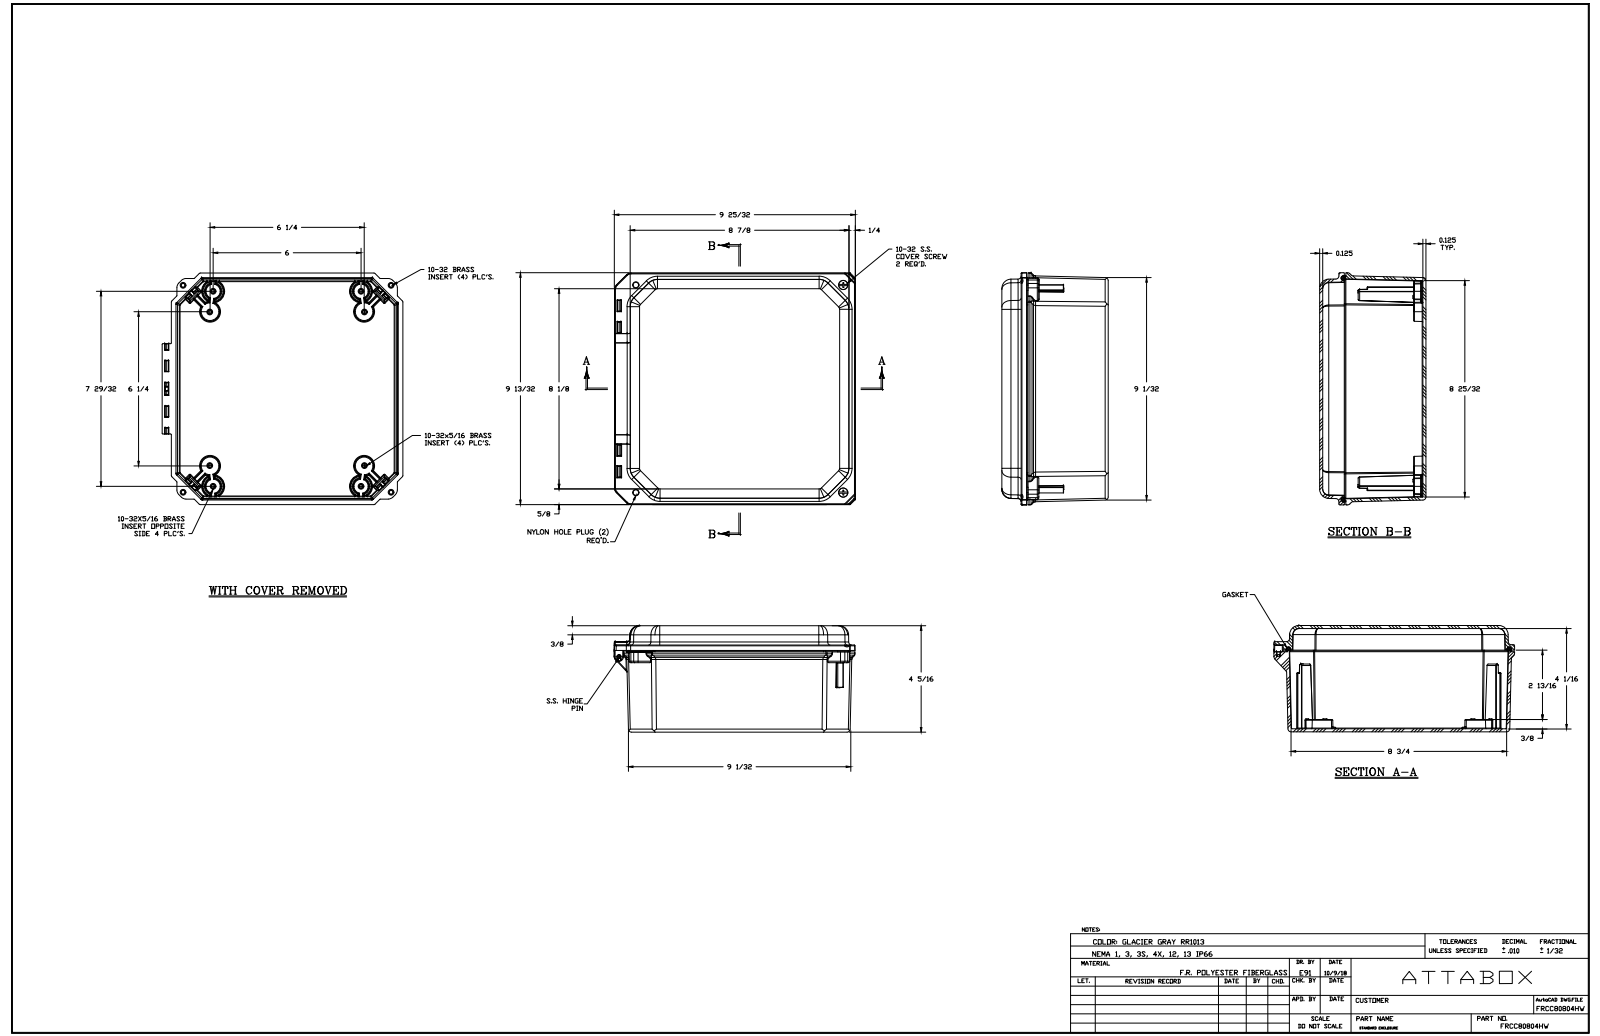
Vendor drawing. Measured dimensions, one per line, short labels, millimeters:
name: FRCC80804HW
written by: SolidWorks 2018 (AUTOMOTIVE_DESIGN)
unit: mm
bodies: 23 solids, 1945 faces (536 planar, 717 cylindrical, 692 other)
size: 248.1 × 238.5 × 109.5
volume: 727 900 mm³; area: 442 800 mm²
holes: 12× ⌀4, 8× ⌀3.9, 4× ⌀5.6, 4× ⌀6.4, 4× ⌀7.9, 2× ⌀3.8, 1× ⌀3.5
bosses: 12× ⌀6.2, 4× ⌀22.1, 2× ⌀11.4, 2× ⌀5.3, 2× ⌀5.1, 1× ⌀3.4
rounds: 140× R0.3, 94× R0.1, 67× R0.5, 37× R0.8, 29× R3.2, 24× R0.8, 24× R2.3, 24× R6.4
face distances: 3.2, 106.3, 109.5, 103.2, 3.1, 89.7, 16.7, 22.2, 86.5, 19.8
hole spacings: 157, 158.8, 188.2, 188.2, 31.3, 38.9, 183.1, 213.7
